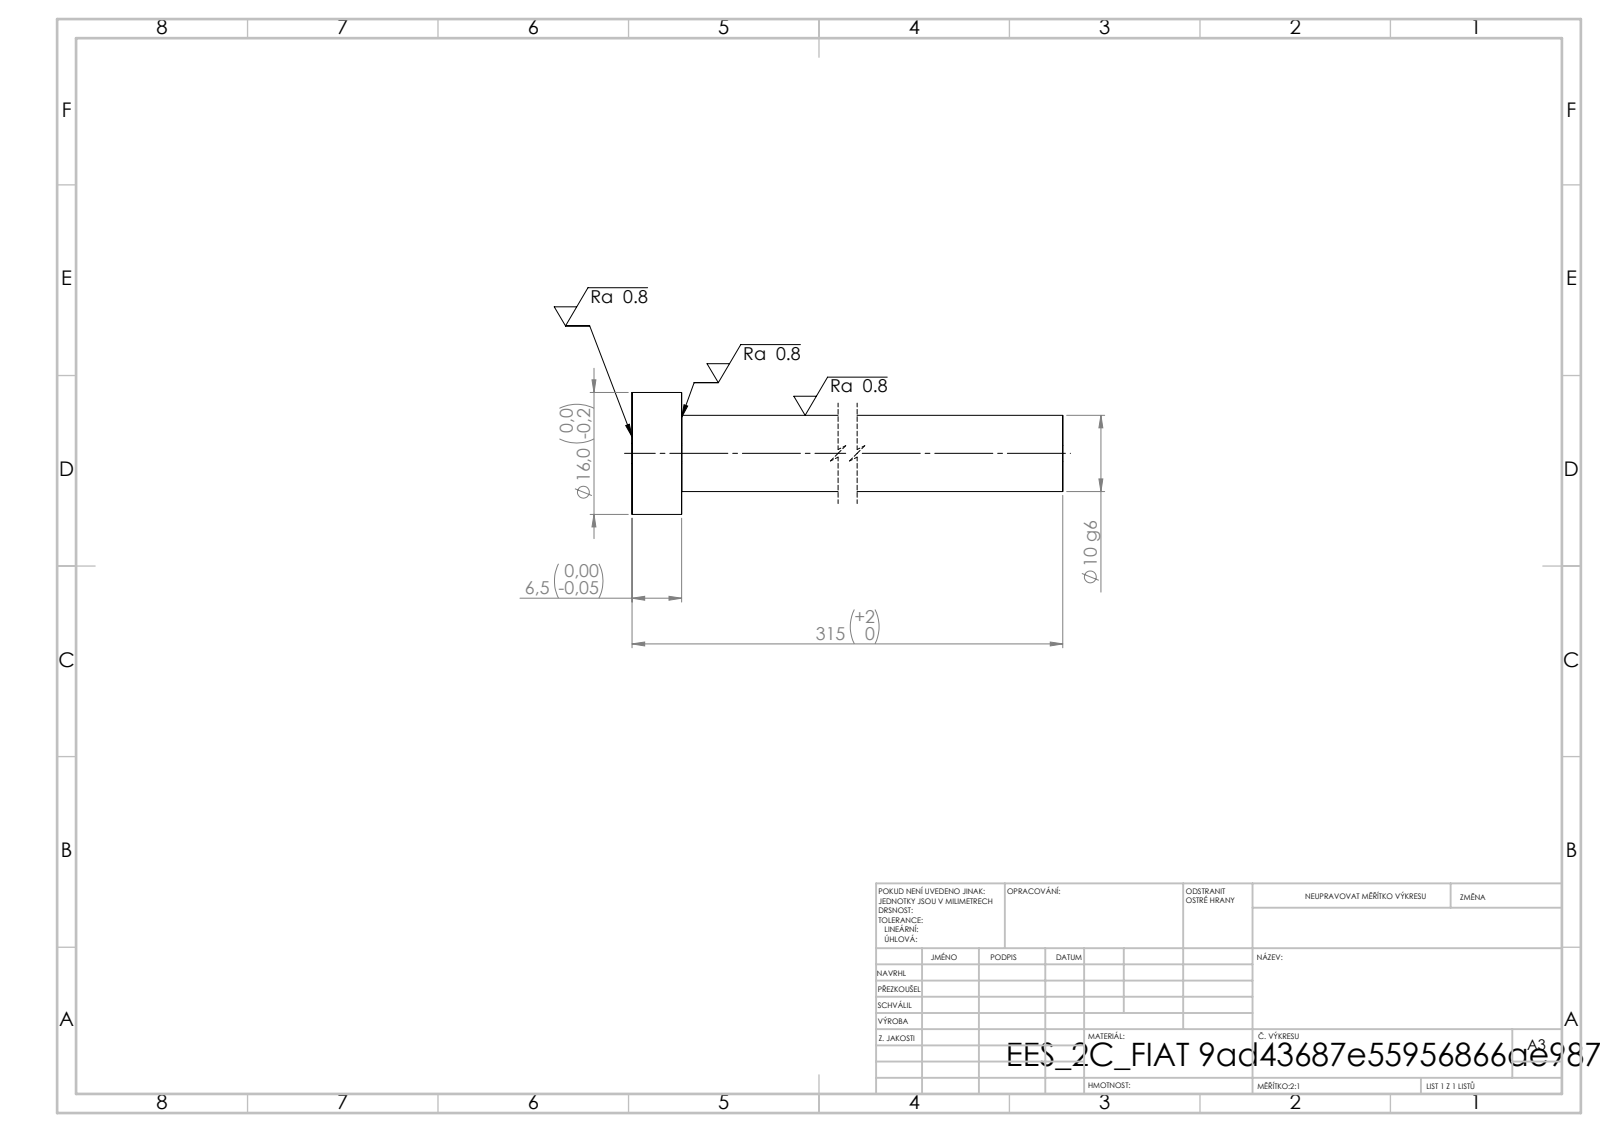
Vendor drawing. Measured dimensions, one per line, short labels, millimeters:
written by: SolidWorks 2019 (CONFIG_CONTROL_DESIGN)
unit: mm
bodies: 1 solid, 7 faces (3 planar, 4 cylindrical, 0 other)
size: 315 × 16 × 16
volume: 25 536 mm³; area: 10 421 mm²
bosses: 1× ⌀16, 1× ⌀10
face distances: 6.5, 315, 308.5
